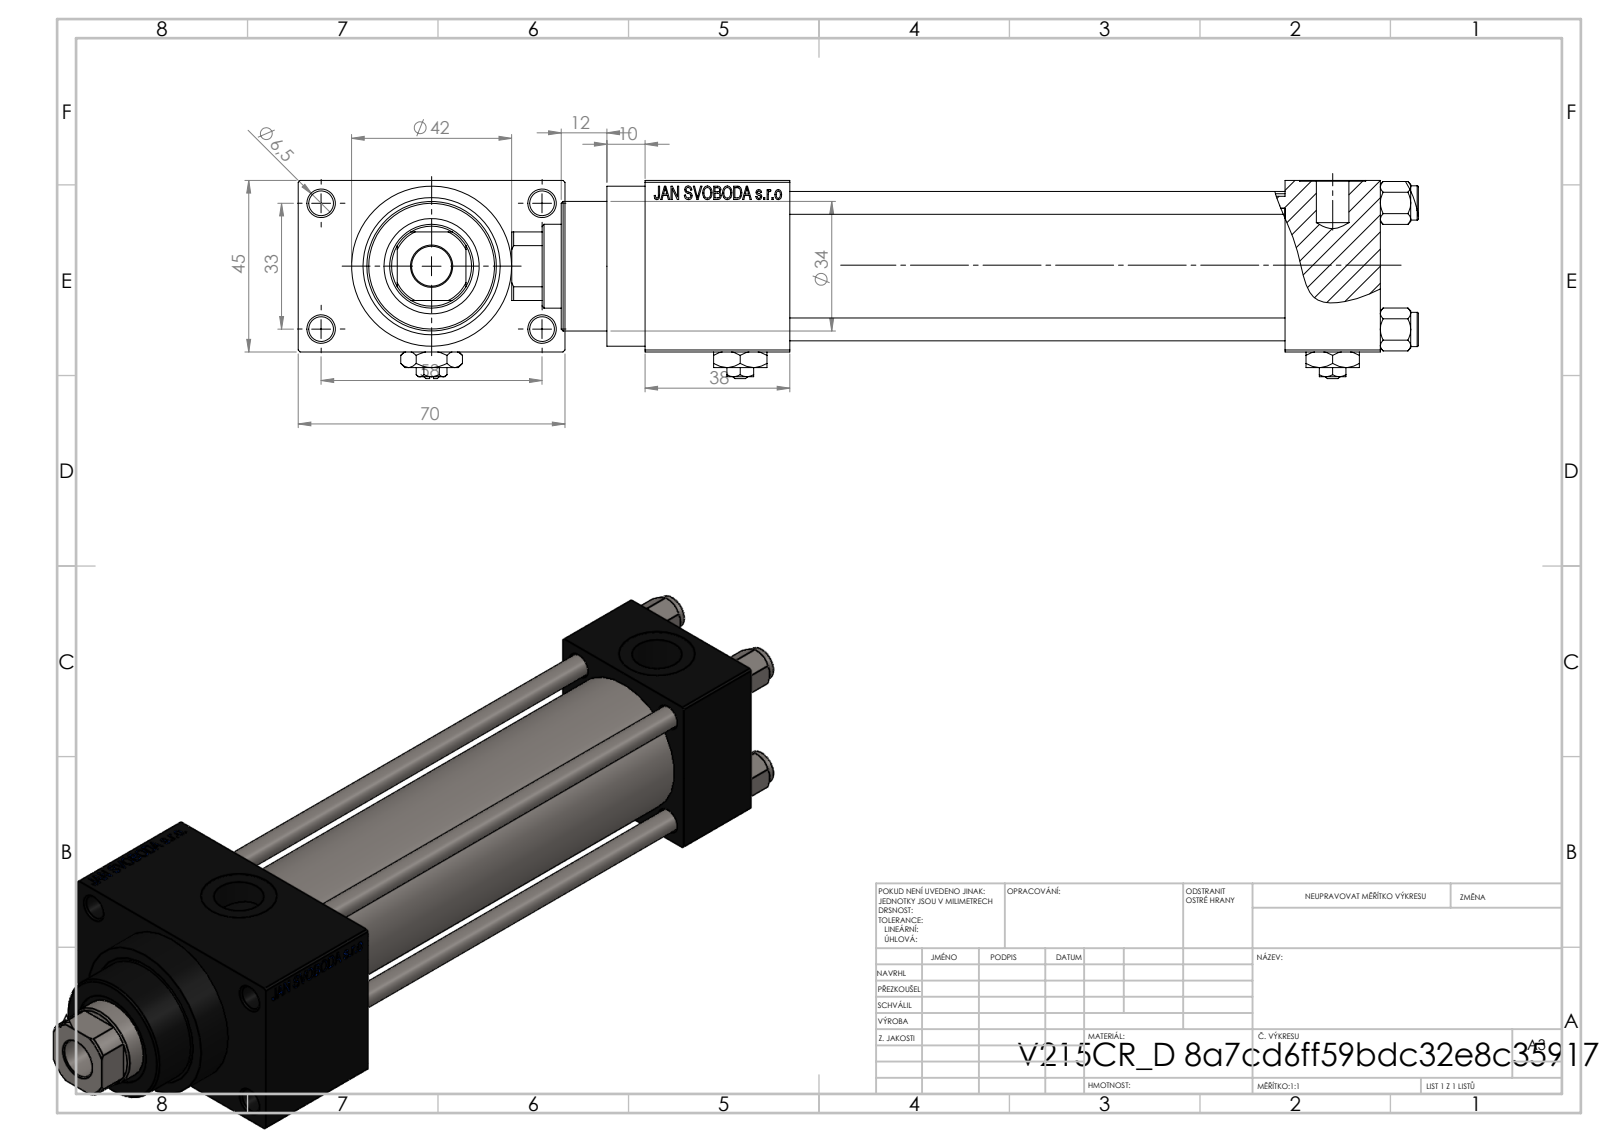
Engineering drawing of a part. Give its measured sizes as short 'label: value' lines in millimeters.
name: V215CR_D_TYCINKA; V215_VC_A; Zatka_pro_OIL_PORT; V215CR_D_Body (+2 more)
written by: SolidWorks 2019 (CONFIG_CONTROL_DESIGN)
unit: mm
bodies: 13 solids, 1204 faces (542 planar, 100 cylindrical, 562 other)
size: 238 × 70 × 52
volume: 309 095 mm³; area: 110 266 mm²
holes: 4× ⌀6, 4× ⌀6.5, 2× ⌀7, 2× ⌀13.16, 2× ⌀20, 1× ⌀10.5, 1× ⌀22, 1× ⌀24, 1× ⌀25, 1× ⌀32, 1× ⌀33
bosses: 4× ⌀9, 1× ⌀42, 1× ⌀38, 1× ⌀34
rounds: 1× R10.5
face distances: 45, 25, 12.5, 57.5, 130, 155, 168, 38, 70, 193
hole spacings: 12.4, 23.48, 33.2, 33.37, 35.35, 45.6, 56.35, 33
